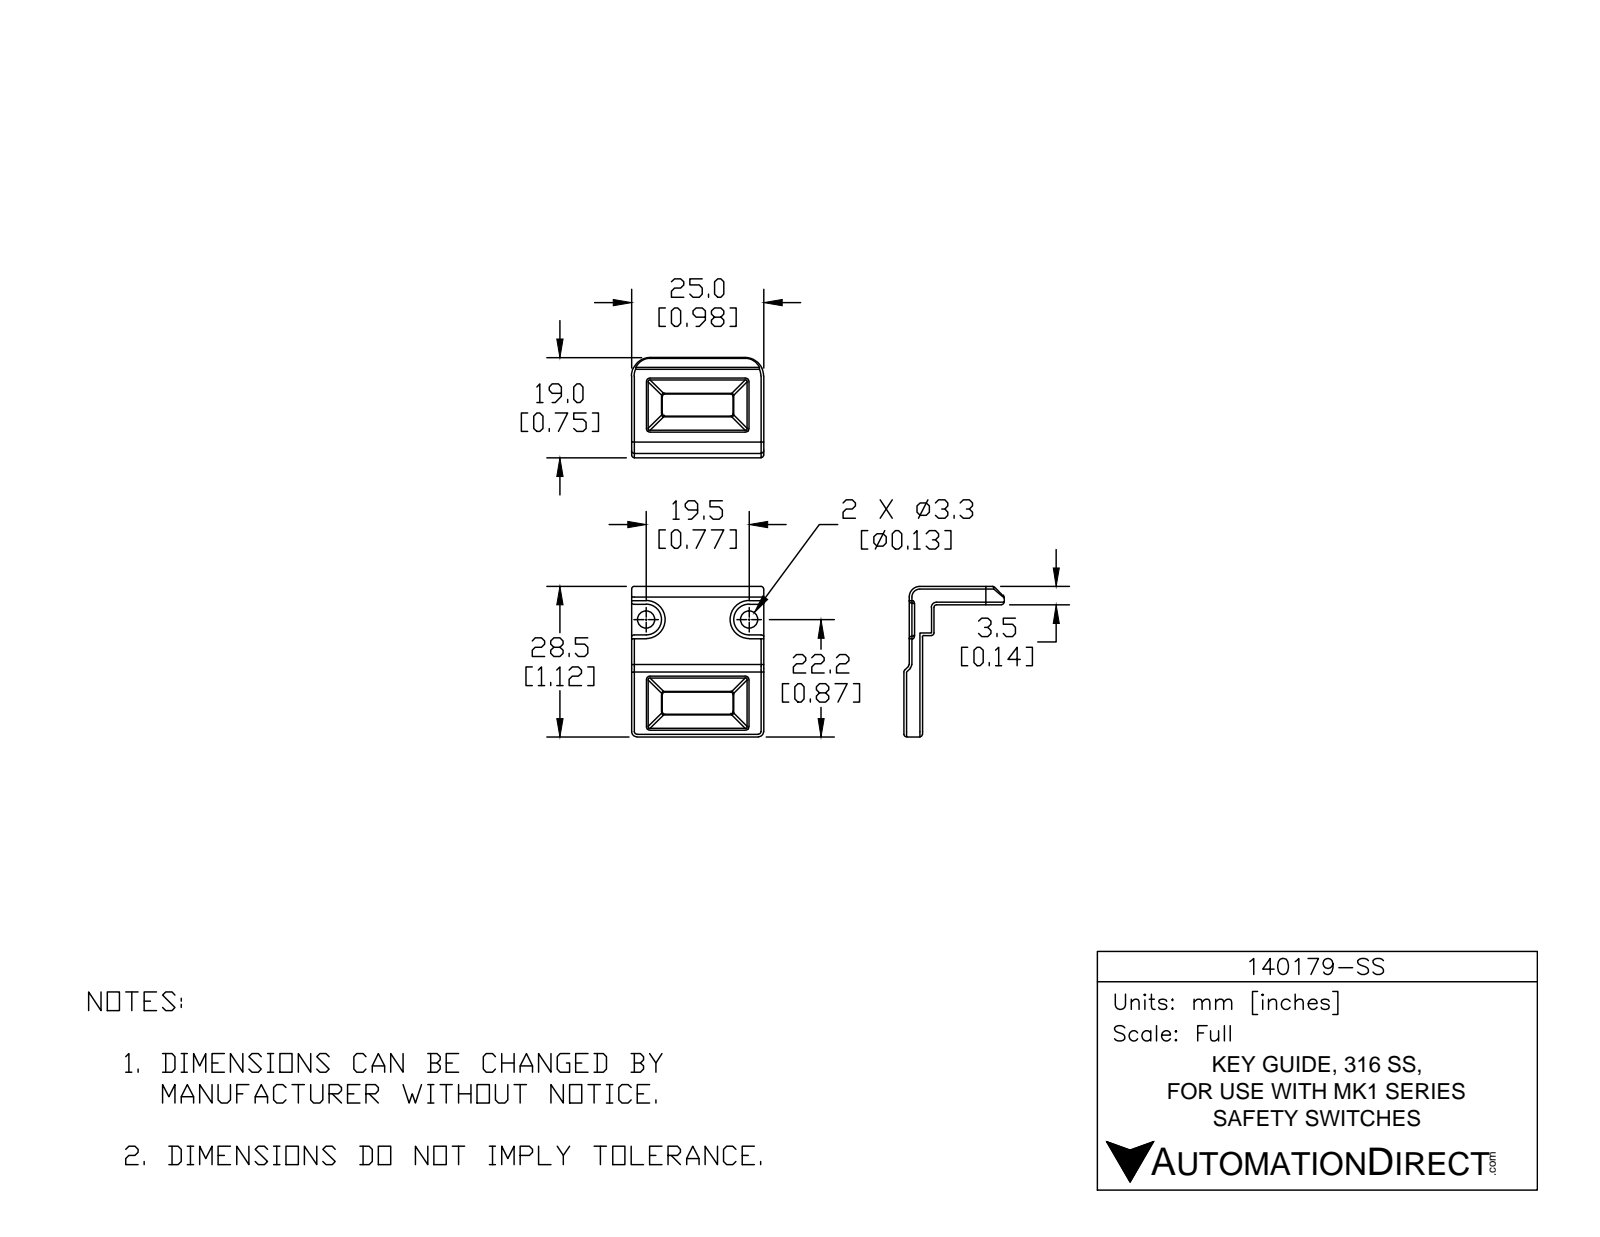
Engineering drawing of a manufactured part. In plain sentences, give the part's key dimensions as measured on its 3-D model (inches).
The part is named "140179-SS". Its 3-D file was written by "SolidWorks 2014 (AUTOMOTIVE_DESIGN)". It is 1 solid with 216 faces: 39 planar, 96 cylindrical and 81 other. Overall it measures 1.122 by 0.984 by 0.748 inches. Its volume is 0.161 cubic inches and its surface area 3.906 square inches. Round holes: 2 of diameter 0.13. Partial cylindrical surfaces (rounded edges, fillets, slot ends): 67 of radius 0.02, 4 of radius 0.012, 2 of radius 0.008, 2 of radius 0.039, 2 of radius 0.118, 2 of radius 0.122, 2 of radius 0.138, 1 of radius 0.079. The main face-to-face distances are 0.098, 0.138, 0.984, 0.039, 1.122, 0.337, 0.621, 0.952, 0.331, 0.059. The hole center spacings are 0.768.
